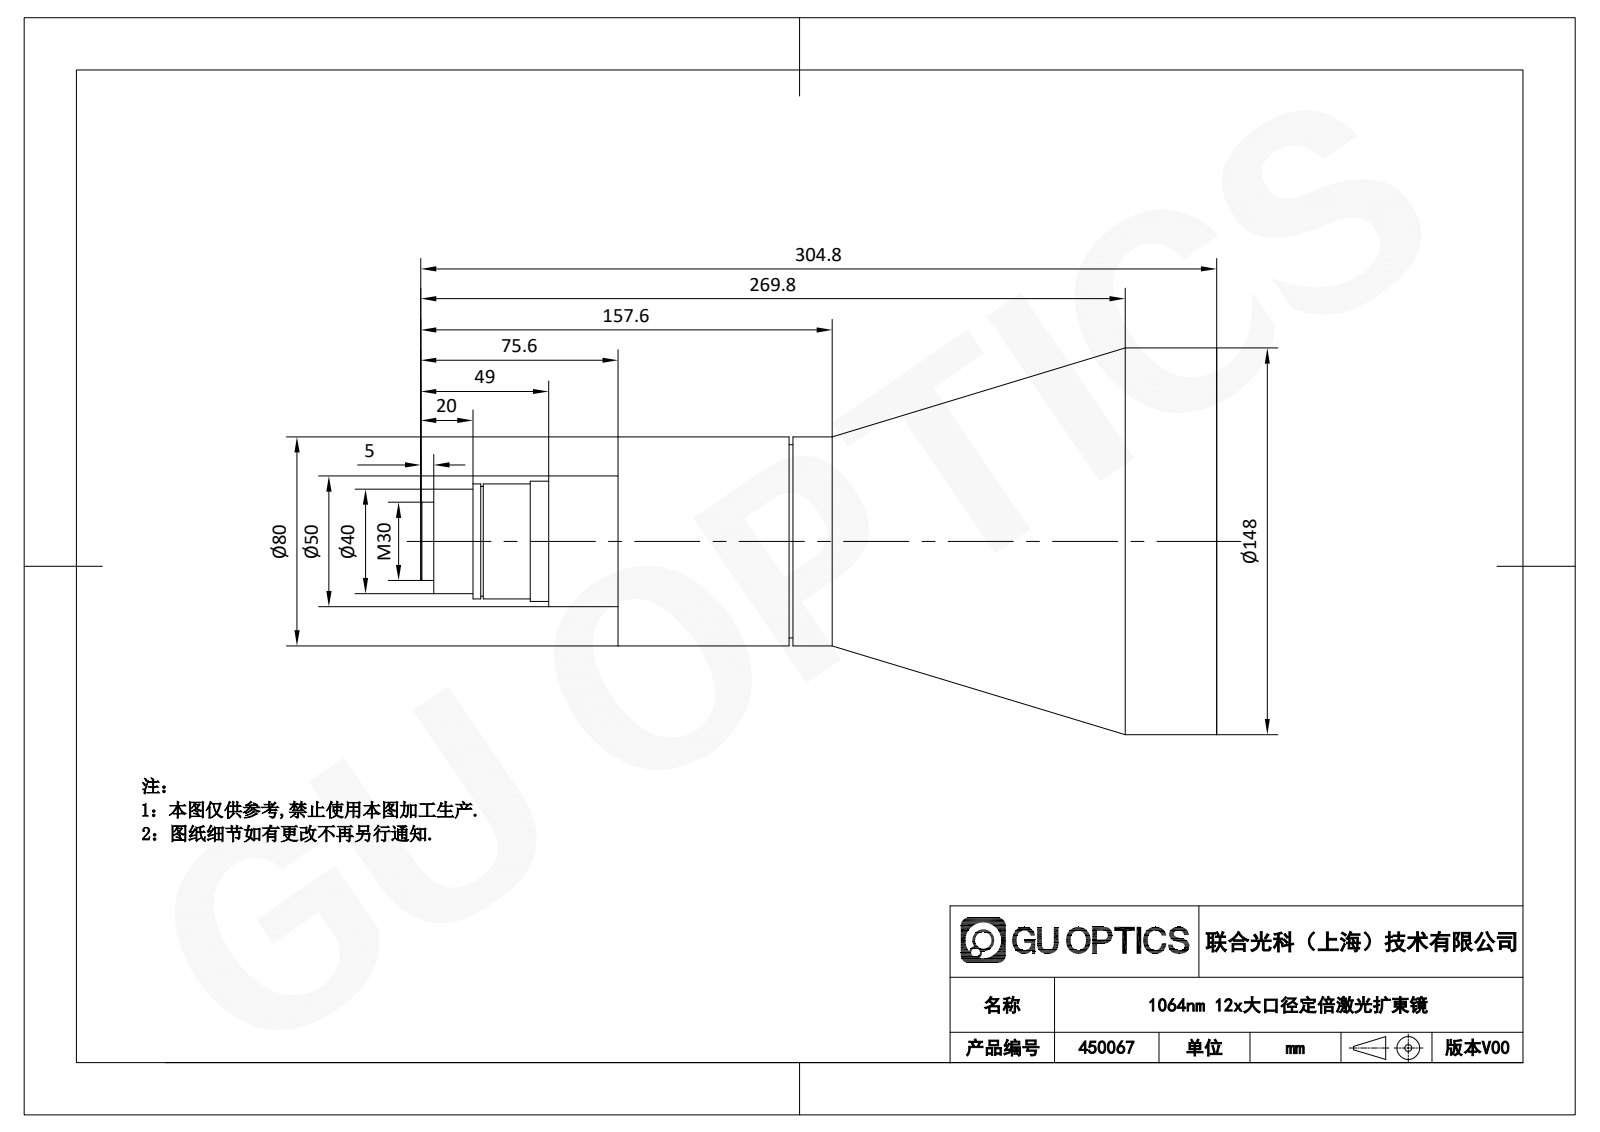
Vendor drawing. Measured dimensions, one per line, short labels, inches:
name: 450067
written by: SolidWorks 2020 (AUTOMOTIVE_DESIGN)
unit: in
bodies: 1 solid, 37 faces (11 planar, 22 cylindrical, 4 other)
size: 12 × 5.827 × 5.827
volume: 141.1 in³; area: 175.7 in²
bosses: 1× ⌀5.827, 1× ⌀3.15, 1× ⌀2.913, 1× ⌀1.969, 1× ⌀1.811, 1× ⌀1.732, 1× ⌀1.654, 1× ⌀1.575
face distances: 9.024, 2.579, 6.445, 2.638, 0.059, 6.386, 2.976, 5.555, 5.614, 12
